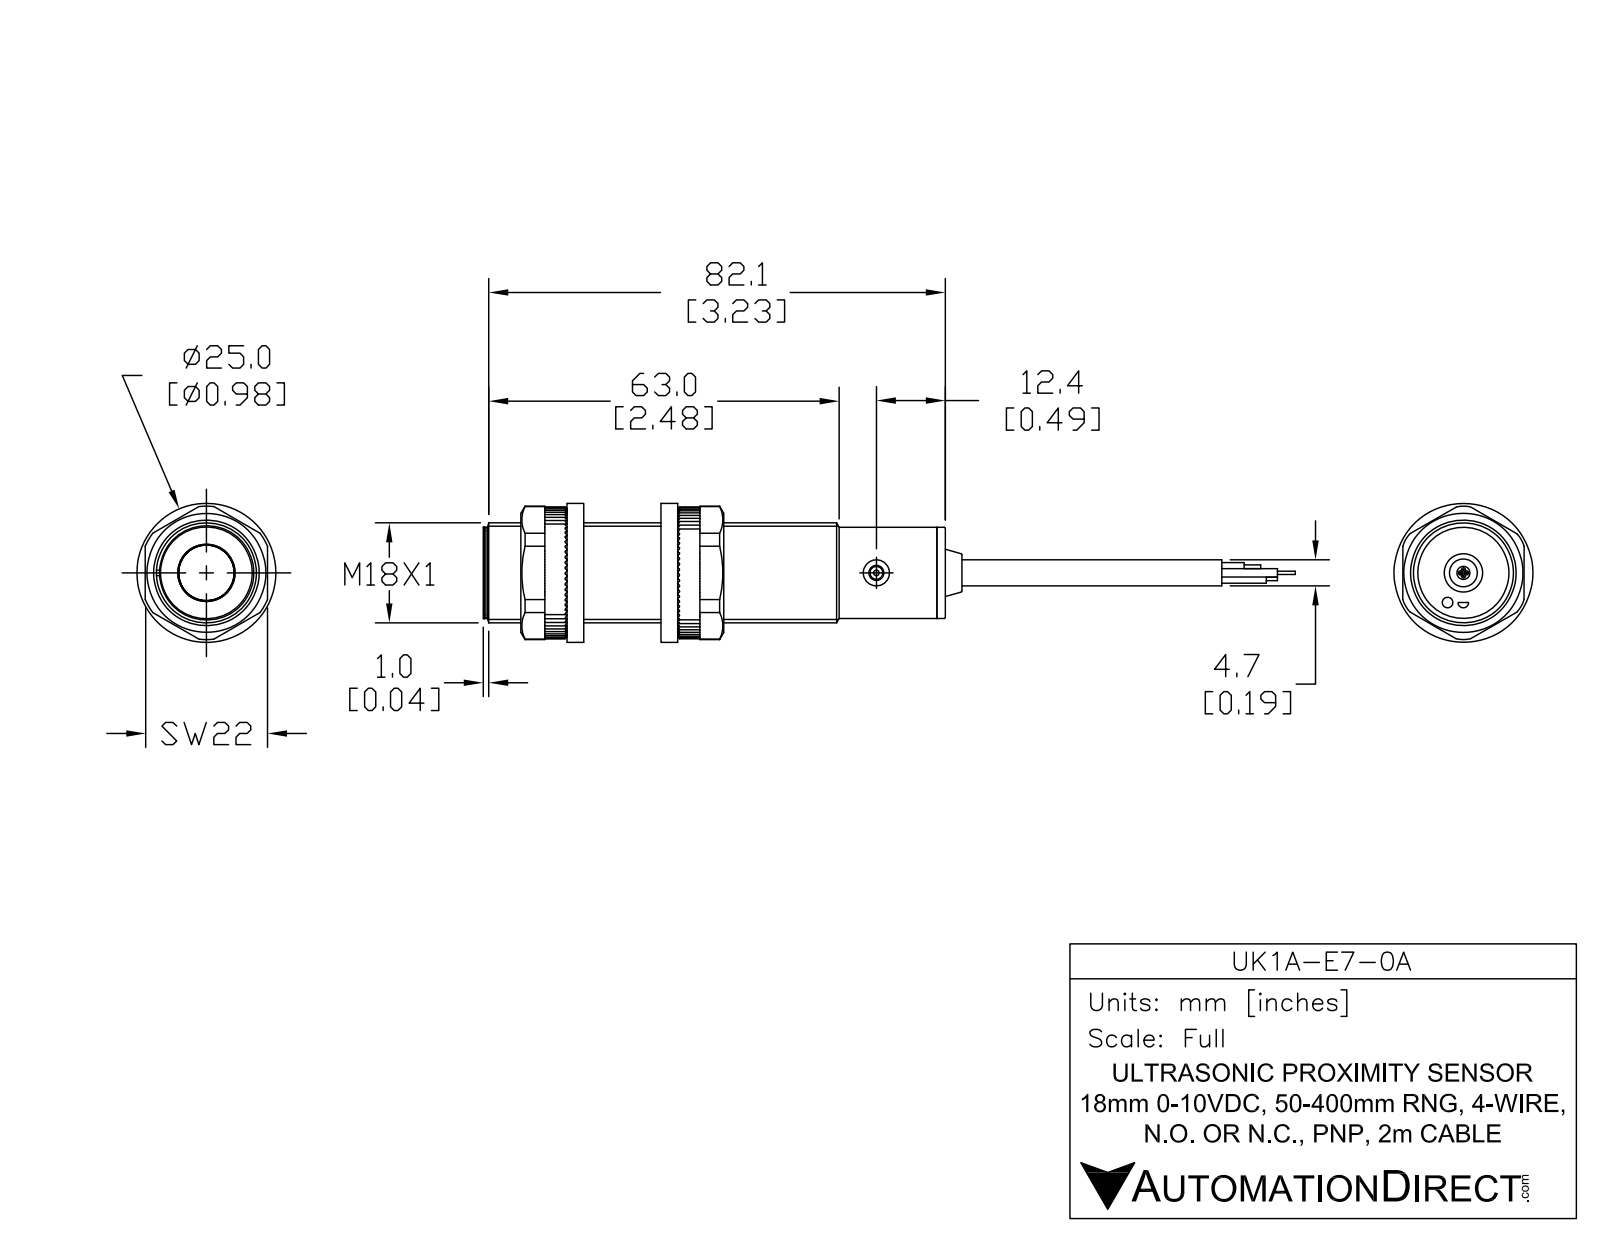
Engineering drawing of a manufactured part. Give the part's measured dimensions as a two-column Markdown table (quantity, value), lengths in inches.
| quantity | value |
| --- | --- |
| part name | UK1A-E7-0A |
| STEP written by | SolidWorks 2017 (AUTOMOTIVE_DESIGN) |
| units | inches |
| bodies | 6 solids, 55 faces (17 planar, 24 cylindrical, 14 other) |
| overall size | 4.832 × 0.709 × 0.709 |
| volume | 1.285 in³ |
| surface area | 10.69 in² |
| round holes (diameter × count) | 0.185 × 2, 0.106 × 1 |
| round bosses / shafts (diameter × count) | 0.709 × 1, 0.646 × 1, 0.622 × 1, 0.374 × 1, 0.189 × 1, 0.091 × 1 |
| main face-to-face distances | 3.193, 3.252, 0.059, 0.039, 3.232, 3.291, 0.041, 3.234, 3.293, 3.257 |
